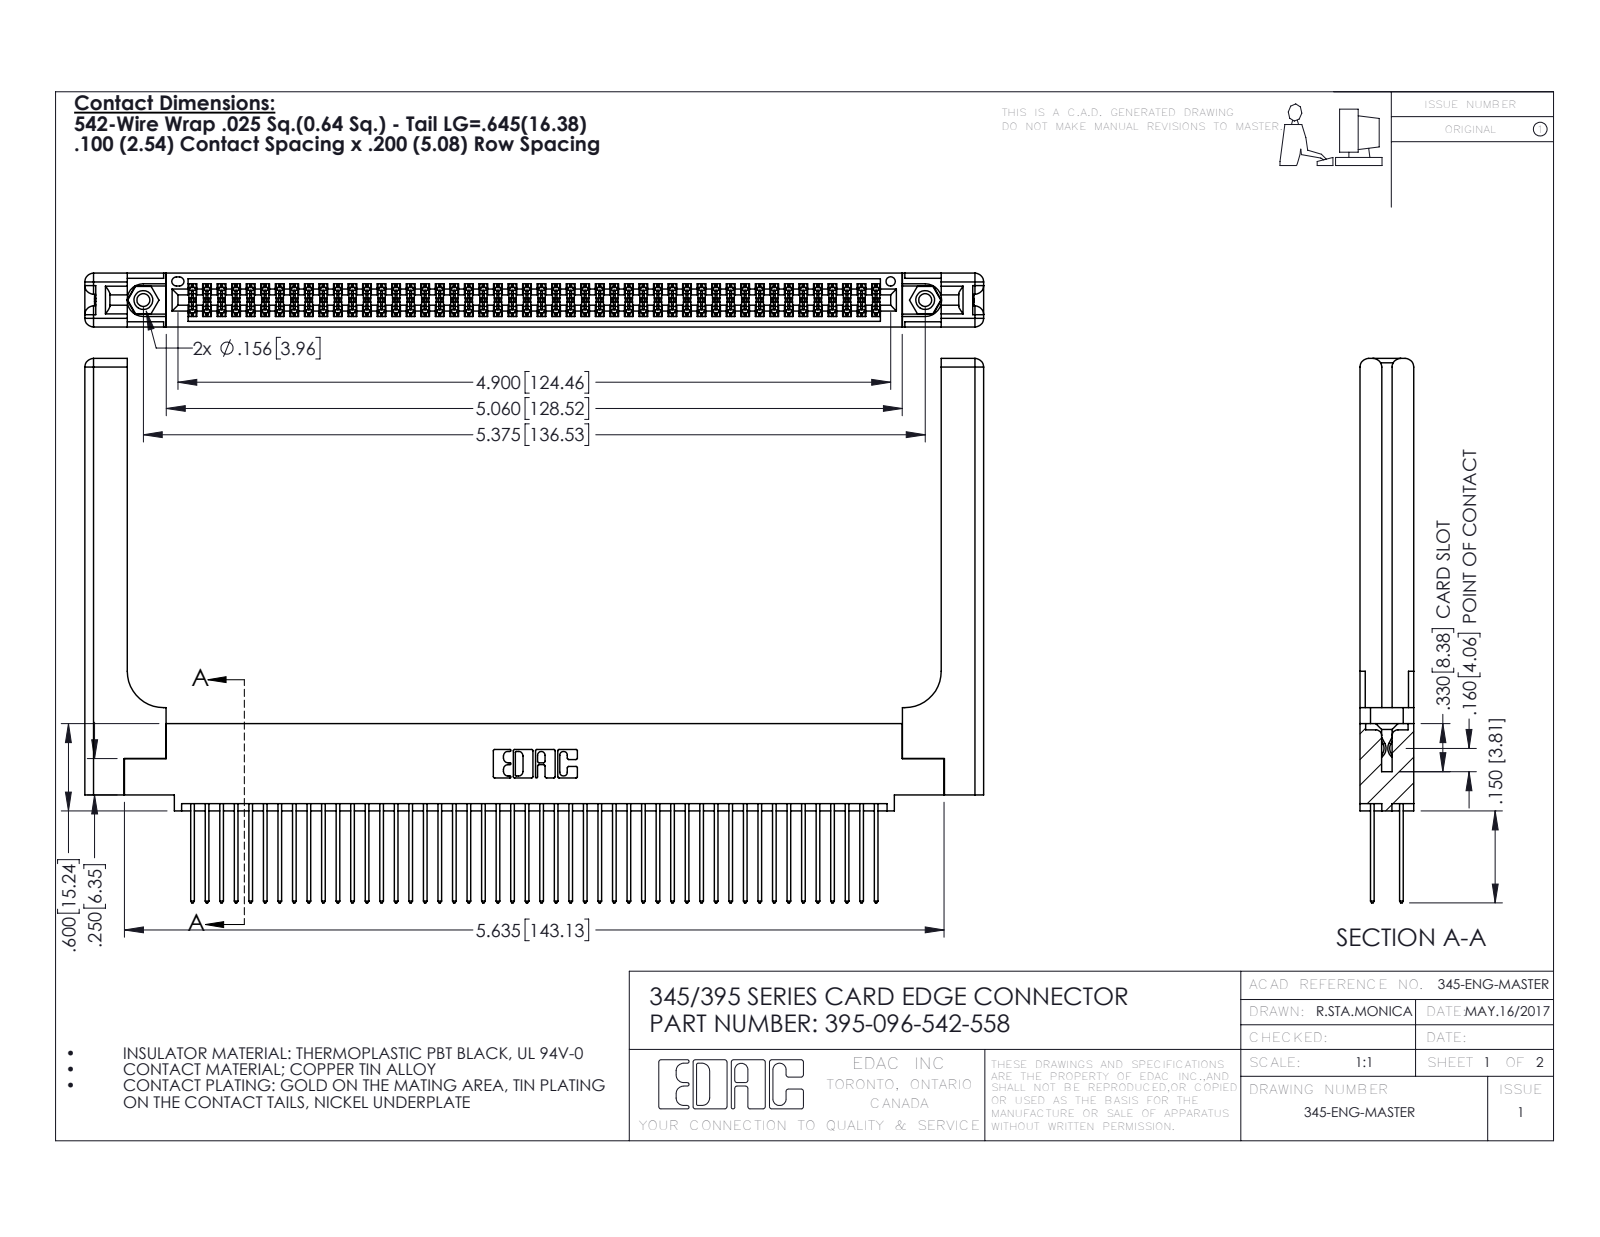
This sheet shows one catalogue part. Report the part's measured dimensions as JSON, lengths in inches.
{"part_name": "395-096-542-558; 345 Part_0.110 Offset - 0.156 Dia-TH; 345-250-001_345-250-001-102; 345-292-001_345-293-142 (+1 more)", "step_written_by": "SolidWorks 2016 (CONFIG_CONTROL_DESIGN)", "units": "inches", "bodies": {"solids": 101, "faces": 5186, "planar": 3400, "cylindrical": 1726, "other": 60}, "overall_size": [6.179, 3.742, 0.37], "volume_in3": 1.474, "surface_area_in2": 47.32, "round_holes": [[0.089, 2], [0.125, 2], [0.156, 2], [0.064, 1]], "round_bosses_or_shafts": [[0.155, 2]], "partial_cylinders_radius": [[0.006, 144], [0.01, 96], [0.01, 22], [0.06, 16], [0.007, 6], [0.031, 6], [0.026, 3], [0.014, 2]], "face_to_face_distances": [0.072, 0.298, 0.37, 0.098, 0.272, 0.025, 0.2, 0.225, 0.175, 0.148], "hole_center_spacings": [0.27, 5.139, 5.375]}
